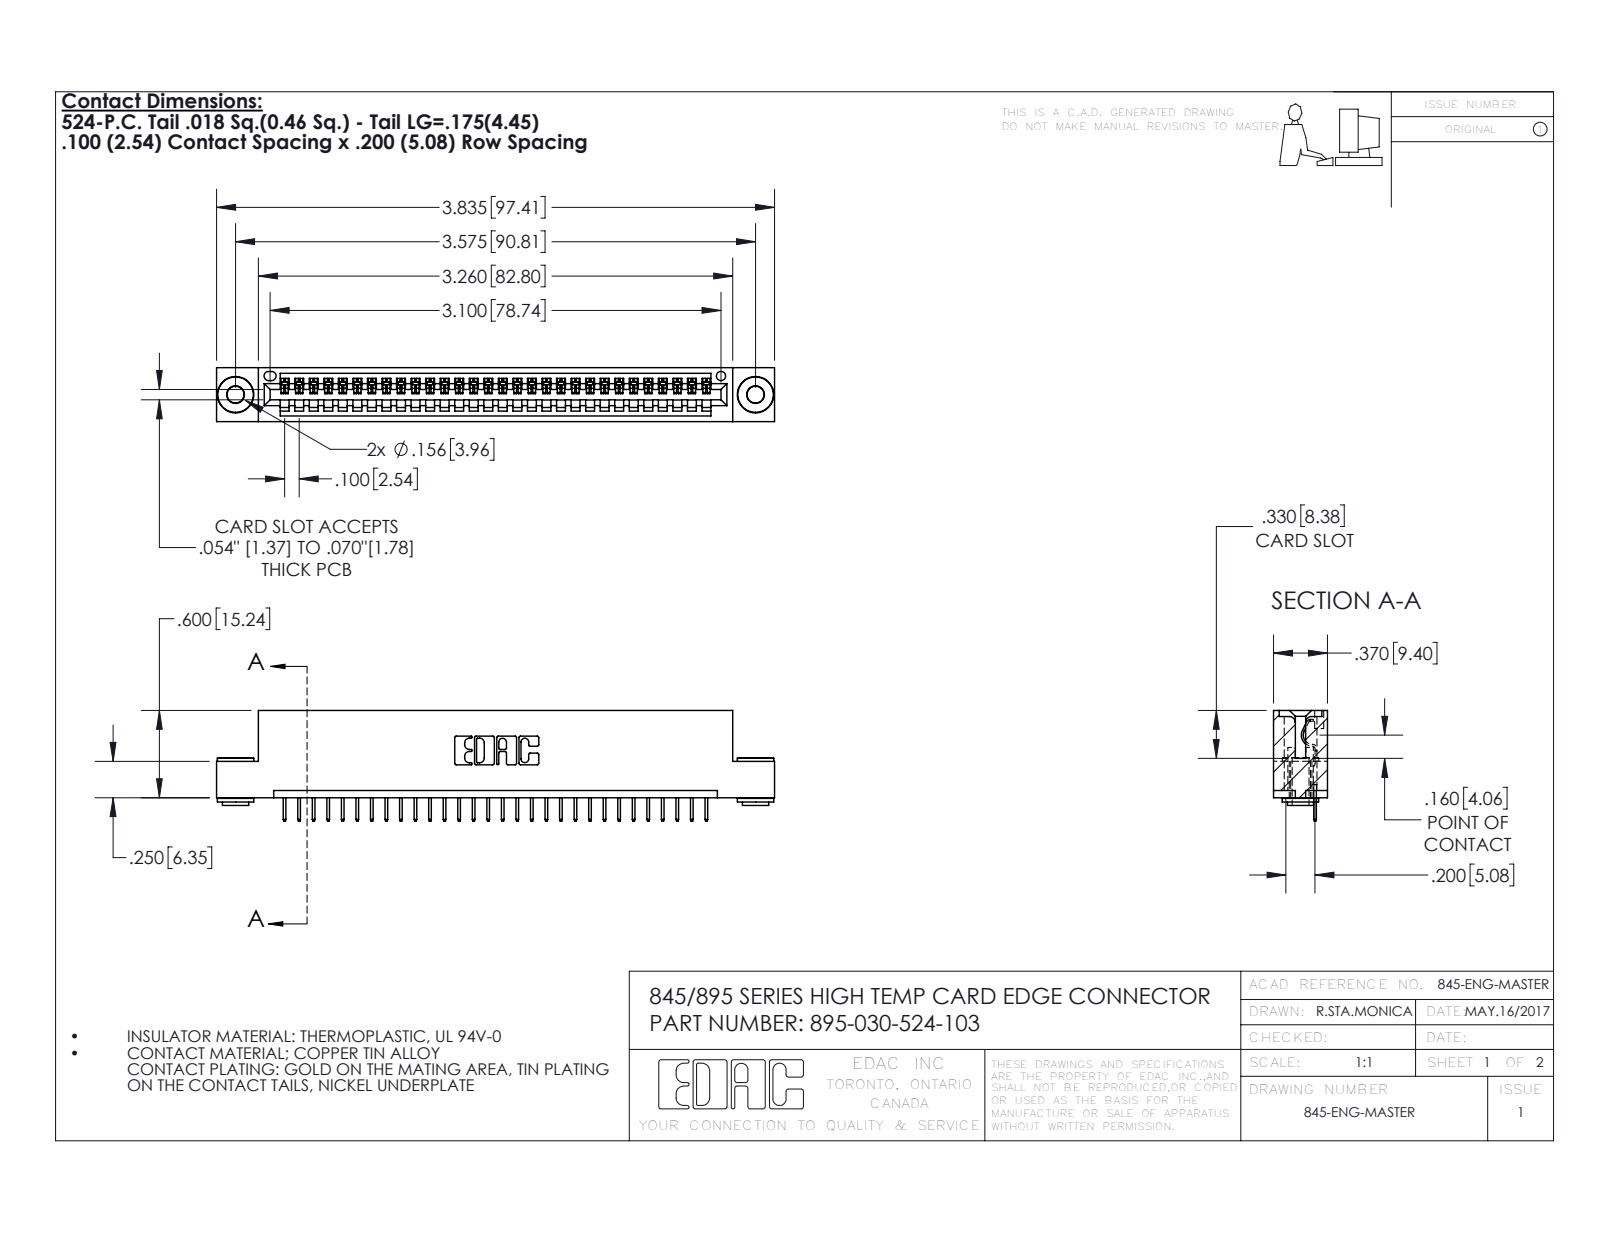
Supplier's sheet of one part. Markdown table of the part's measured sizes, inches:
| quantity | value |
| --- | --- |
| part name | 345-250-002_345-250-002-102; 345 Part_Flush Mounting Lugs - 0.156 Dia-TH; 345-292-001_345-293-124; 395-030-524-103 |
| STEP written by | SolidWorks 2016 (CONFIG_CONTROL_DESIGN) |
| units | inches |
| bodies | 33 solids, 2024 faces (1470 planar, 546 cylindrical, 8 other) |
| overall size | 3.835 × 0.762 × 0.37 |
| volume | 0.553 in³ |
| surface area | 18.14 in² |
| round holes (diameter × count) | 0.116 × 2, 0.156 × 2, 0.064 × 1 |
| round bosses / shafts (diameter × count) | 0.25 × 2, 0.18 × 2, 0.136 × 2 |
| partial cylindrical surfaces (radius × count) | 0.006 × 60, 0.01 × 22, 0.007 × 6, 0.031 × 6, 0.026 × 3, 0.031 × 2, 0.04 × 2, 0.014 × 1 |
| main face-to-face distances | 0.072, 0.298, 0.37, 0.2, 0.025, 0.098, 0.272, 0.225, 0.072, 0.149 |
| hole center spacings | 0.27, 3.34, 3.575 |
